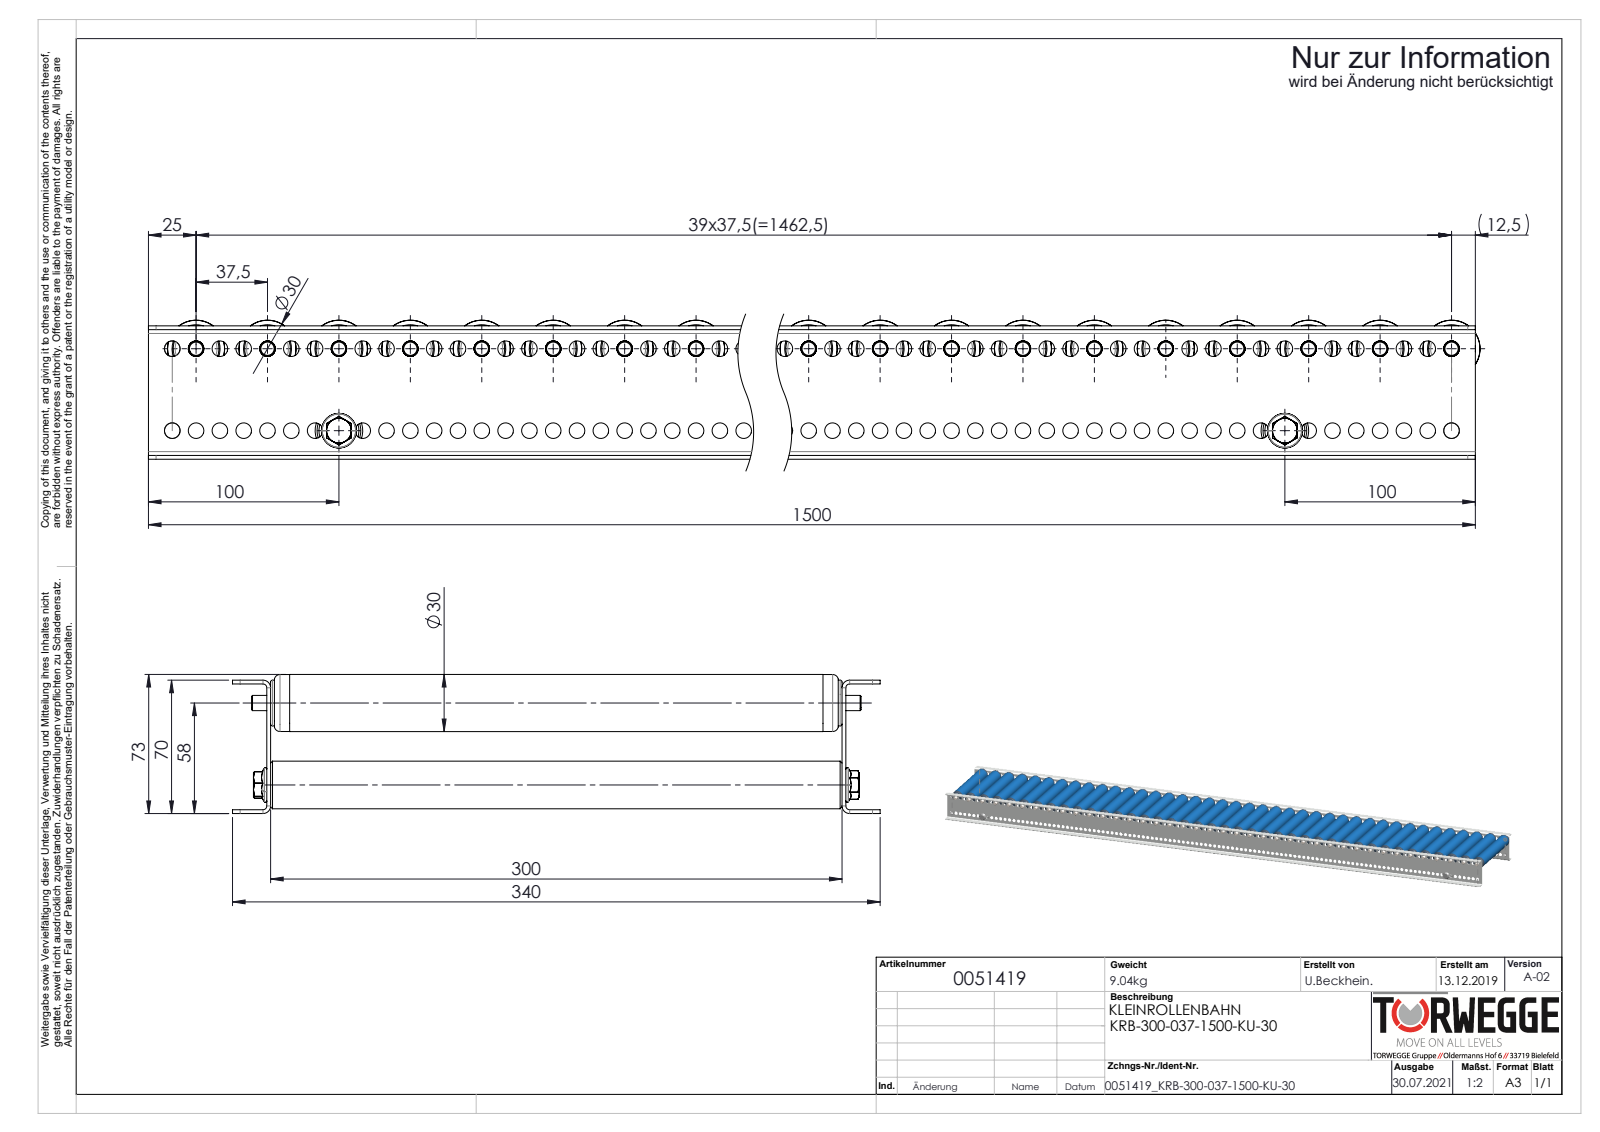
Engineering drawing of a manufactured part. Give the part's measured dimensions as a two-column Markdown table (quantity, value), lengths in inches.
| quantity | value |
| --- | --- |
| part name | 0017013_Tragrollenrohr-Ø30x1,8KU_KFG_0017012_L=280; Traversen_KFG_L300; KUT50-30x1,8-KB-A8-FA_KFG_0034505TWG_KUT50-30x1,8-KB-A8-FA-EL=300; 0051419 (+4 more) |
| STEP written by | SolidWorks 2020 (AUTOMOTIVE_DESIGN) |
| units | inches |
| bodies | 92 solids, 9472 faces (2920 planar, 3568 cylindrical, 2984 other) |
| overall size | 59.154 × 13.386 × 2.874 |
| volume | 190 in³ |
| surface area | 5 419 in² |
| round holes (diameter × count) | 0.323 × 238, 0.319 × 40, 0.89 × 40, 0.992 × 40, 0.268 × 2, 0.827 × 2 |
| round bosses / shafts (diameter × count) | 0.315 × 42, 1.181 × 40, 1.177 × 40, 1.043 × 40, 1.039 × 40, 0.945 × 40, 0.984 × 2 |
| partial cylindrical surfaces (radius × count) | 0.199 × 40, 0.157 × 8, 0.079 × 4 |
| main face-to-face distances | 0.079, 11.89, 11.811, 2.677, 11.969, 2.756, 2.598, 0.394, 11.417, 0.472 |
| hole center spacings | 0.492, 0.984, 1.476, 1.969, 2.461, 2.953, 3.445, 3.937 |
